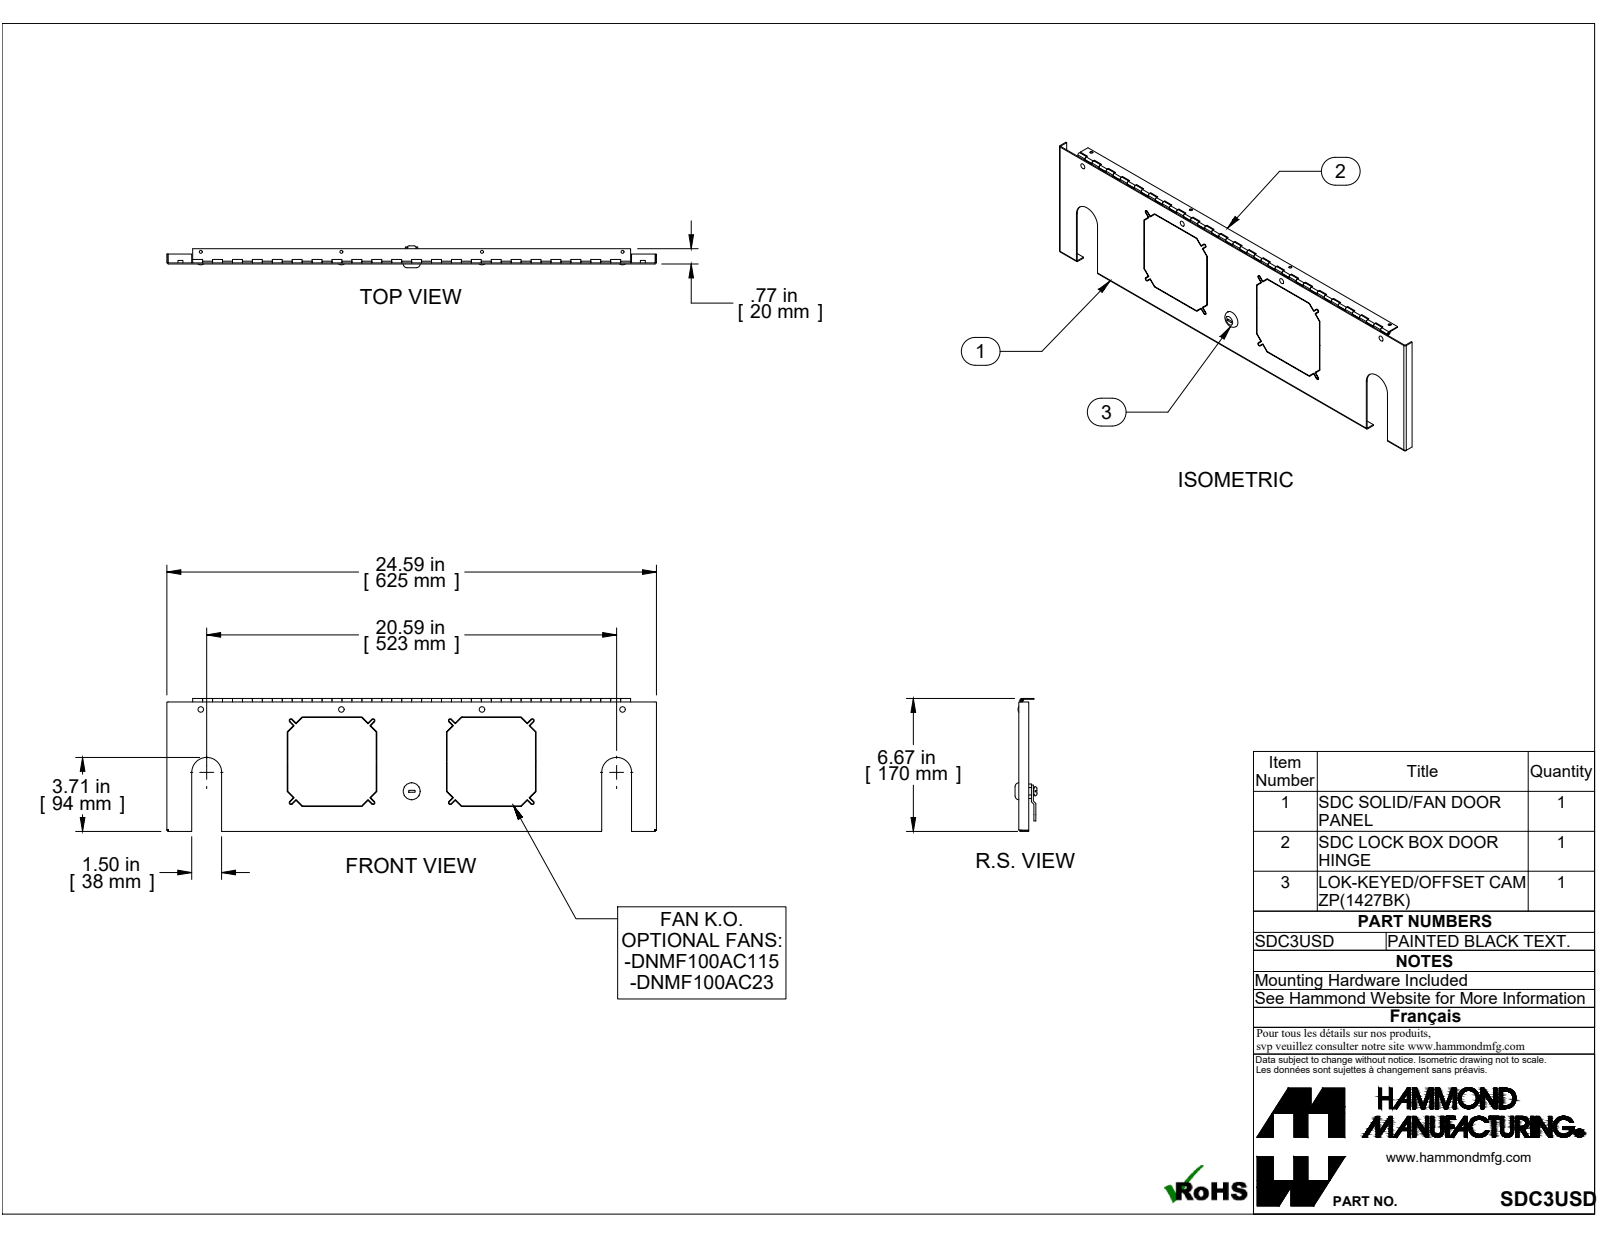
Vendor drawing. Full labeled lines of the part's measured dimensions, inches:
Part name (STEP PRODUCT): SDC3USD
STEP written by: SolidWorks 2019 (CONFIG_CONTROL_DESIGN)
Units: inches
Bodies: 15 solids, 570 faces (412 planar, 142 cylindrical, 16 other)
Overall size (bounding box): 24.594 × 6.674 × 1.1
Volume: 11.36 in³ · Surface area: 419.1 in²
Round holes (diameter × count): ⌀0.15 ×8, ⌀0.126 ×4, ⌀0.092 ×1, ⌀0.125 ×1, ⌀0.204 ×1, ⌀0.597 ×1
Round bosses / shafts (diameter × count): ⌀0.728 ×1, ⌀0.232 ×1, ⌀0.174 ×1, ⌀0.08 ×1
Partial cylindrical surfaces — rounded edges, fillets, slot ends (radius × count): R0.064 ×8, R0.094 ×8, R0.029 ×3, R0.086 ×3, R0.31 ×2, R0.75 ×2, R0.38 ×1
Main face-to-face distances: 0.057, 0.041, 0.098, 6.576, 6.617, 6.633, 6.674, 0.057, 24.537, 24.48
Hole centre spacings: 7.063, 14.125, 5.417, 6.657, 7.062, 11.362, 12.003, 21.187
